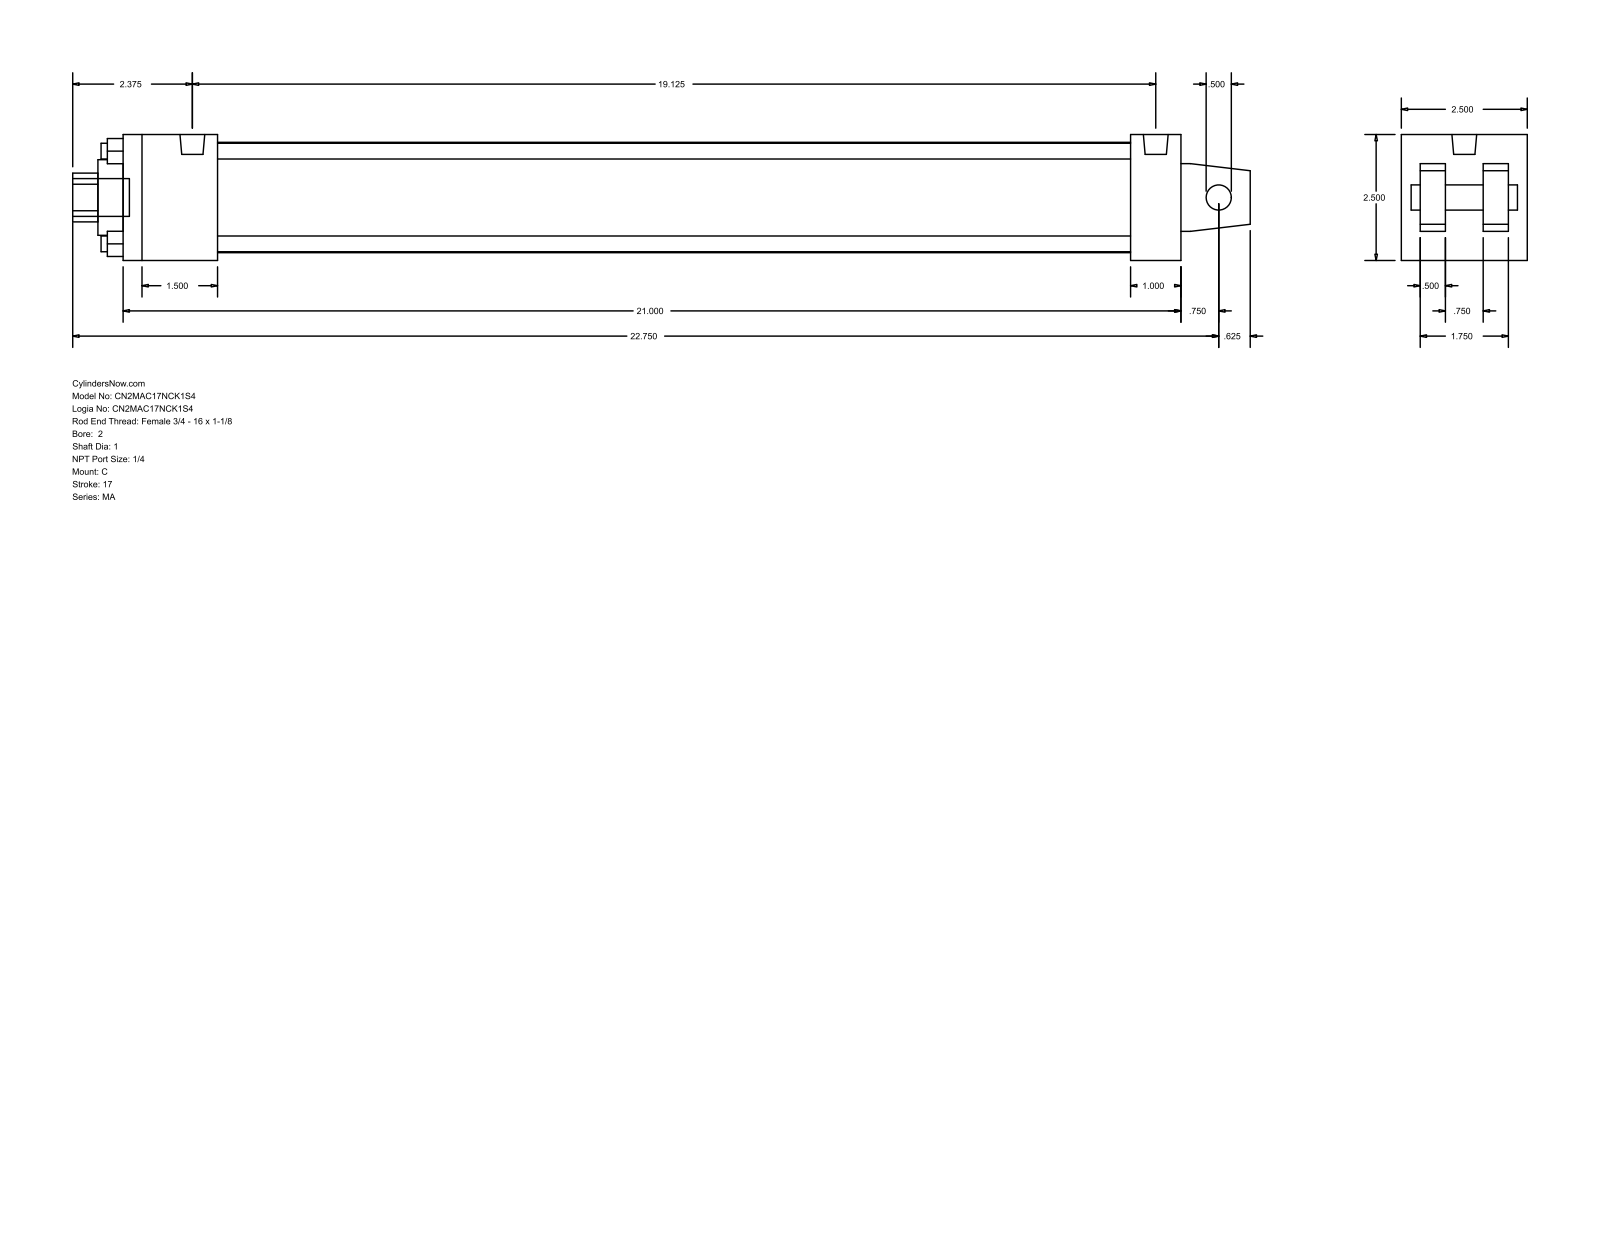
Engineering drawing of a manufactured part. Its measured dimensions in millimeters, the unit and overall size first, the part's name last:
Units: millimetres
Overall size (bounding box): 593.73 × 63.5 × 63.5
Round holes (diameter × count): ⌀7.94 ×4, ⌀12.7 ×1, ⌀25.4 ×1, ⌀38.1 ×1, ⌀55.63 ×1
Round bosses / shafts (diameter × count): ⌀7.94 ×4, ⌀12.49 ×2, ⌀19.05 ×1
Partial cylindrical surfaces — rounded edges, fillets, slot ends (radius × count): R12.29 ×1
Main face-to-face distances: 63.5, 12.7, 533.4, 22.22, 41.28, 9.52, 53.98, 31.76, 47.63, 25.4
Hole centre spacings: 33.05, 46.74, 66.1
Bodies: 0 solids, 103 faces (76 planar, 27 cylindrical, 0 other)
Part name (STEP PRODUCT): MA_C__0200_1
STEP written by: GSSL Pune (CONFIG_CONTROL_DESIGN)
